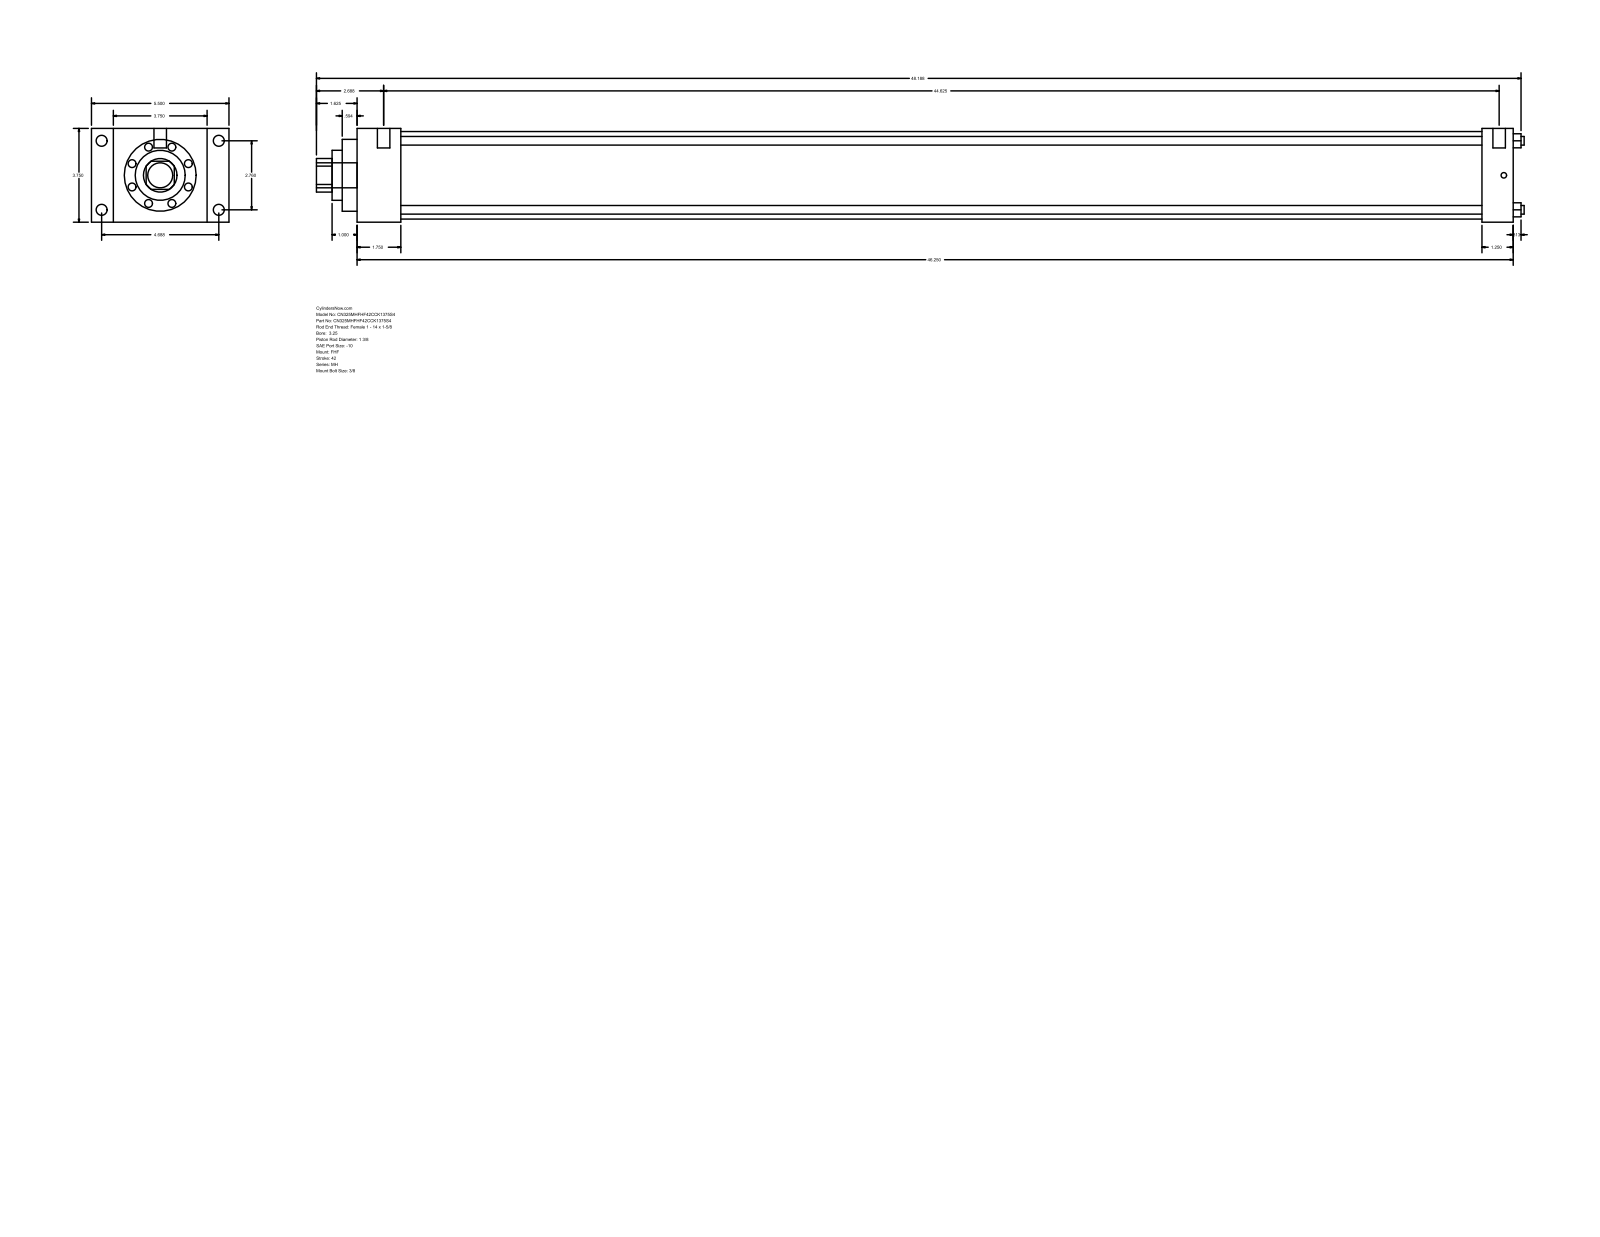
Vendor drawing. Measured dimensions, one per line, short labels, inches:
name: MH_FHF__0325_1.375
written by: GSSL Pune (CONFIG_CONTROL_DESIGN)
unit: in
bodies: 0 solids, 90 faces (61 planar, 29 cylindrical, 0 other)
size: 48.313 × 5.5 × 3.75
holes: 4× ⌀0.345, 1× ⌀1.375, 1× ⌀2, 1× ⌀2.875, 1× ⌀3.5
bosses: 4× ⌀0.438, 4× ⌀0.219, 2× ⌀0.5, 1× ⌀1
rounds: 1× R0.672
face distances: 3.75, 46.25, 1.75, 44.5, 0.875, 4.625, 5.5, 45, 43.25, 1.25
hole spacings: 1.952, 2.76, 3.903
